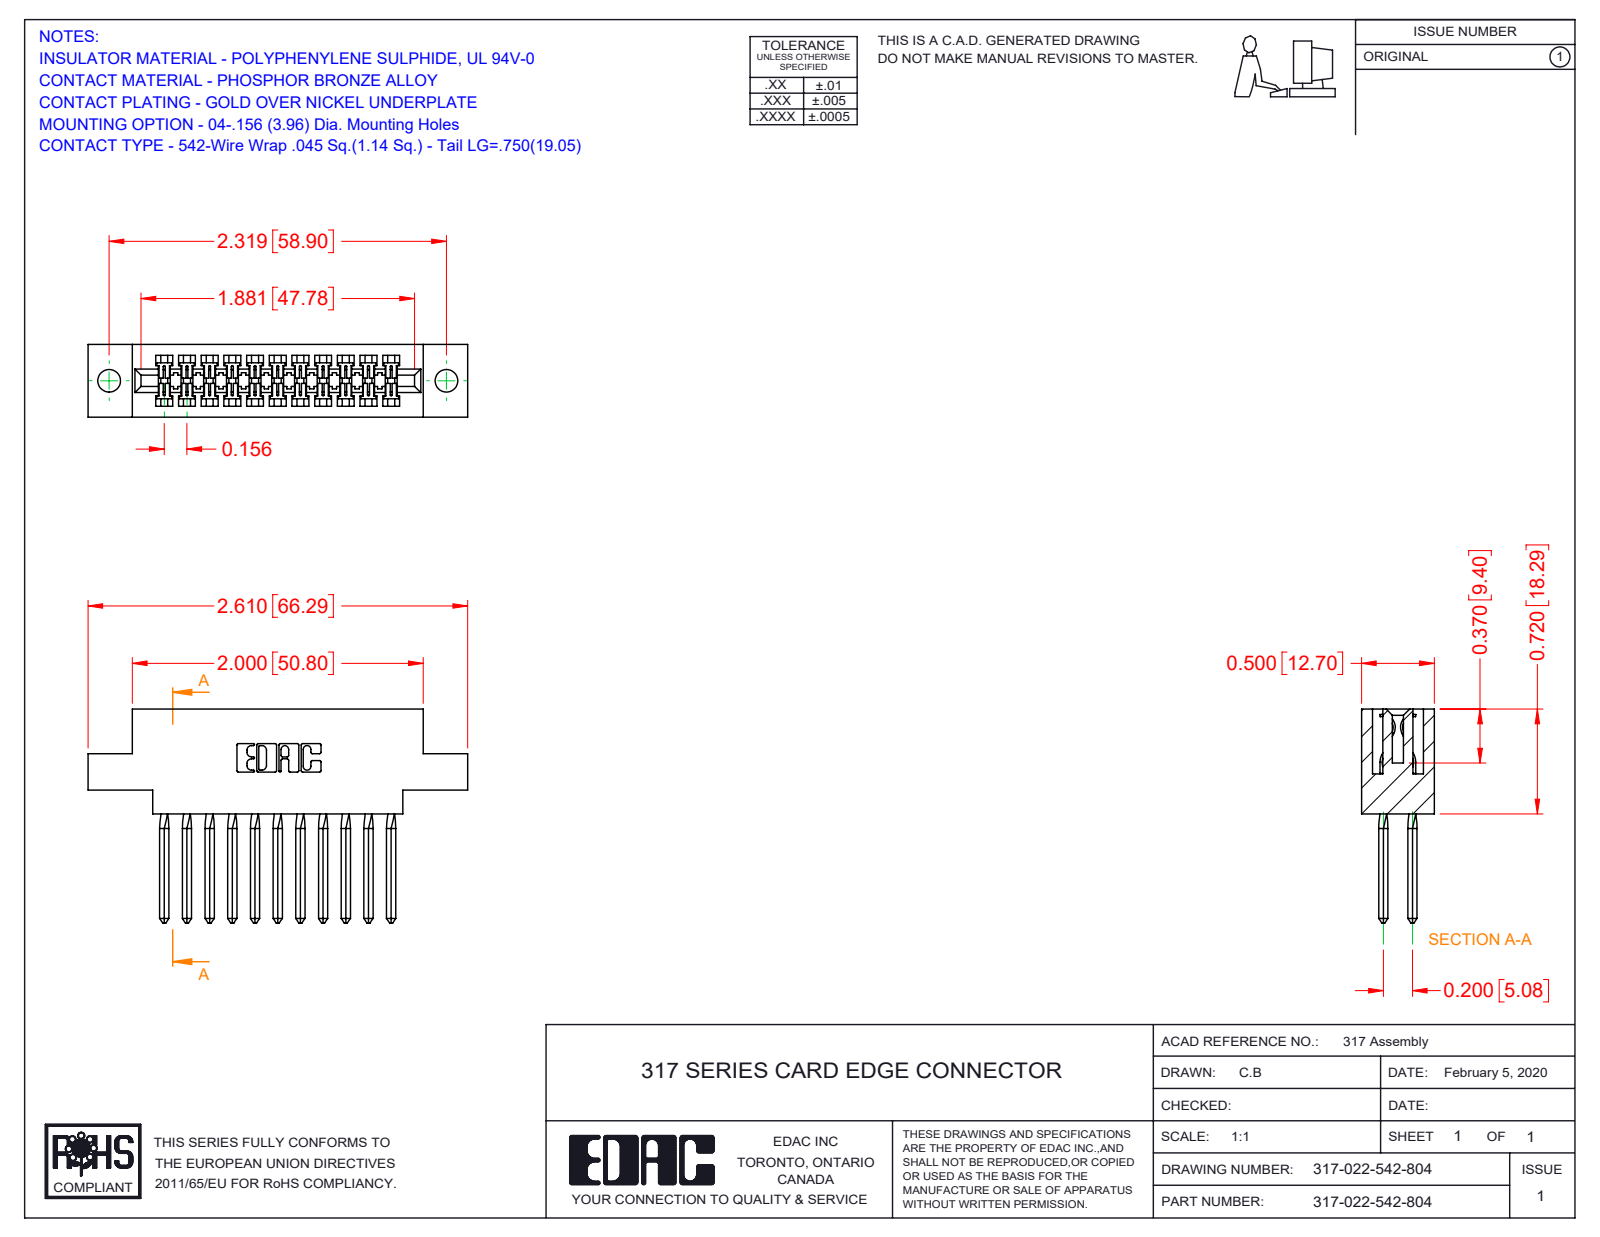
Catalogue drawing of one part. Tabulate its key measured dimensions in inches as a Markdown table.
| quantity | value |
| --- | --- |
| part name | 317 Part_.156 Dia - TH; 317-022-542-804; 317-290-003_542 |
| STEP written by | SolidWorks 2016 (CONFIG_CONTROL_DESIGN) |
| units | inches |
| bodies | 23 solids, 1356 faces (1070 planar, 198 cylindrical, 88 other) |
| overall size | 2.61 × 1.47 × 0.5 |
| volume | 0.597 in³ |
| surface area | 19.27 in² |
| round holes (diameter × count) | 0.156 × 2 |
| partial cylindrical surfaces (radius × count) | 0.006 × 44, 0.01 × 22, 0.007 × 6, 0.031 × 6, 0.026 × 3, 0.074 × 2, 0.089 × 2, 0.1 × 2 |
| main face-to-face distances | 0.5, 0.075, 0.425, 0.11, 0.116, 0.22, 0.35, 0.2, 0.136, 0.156 |
| hole center spacings | 2.319 |
